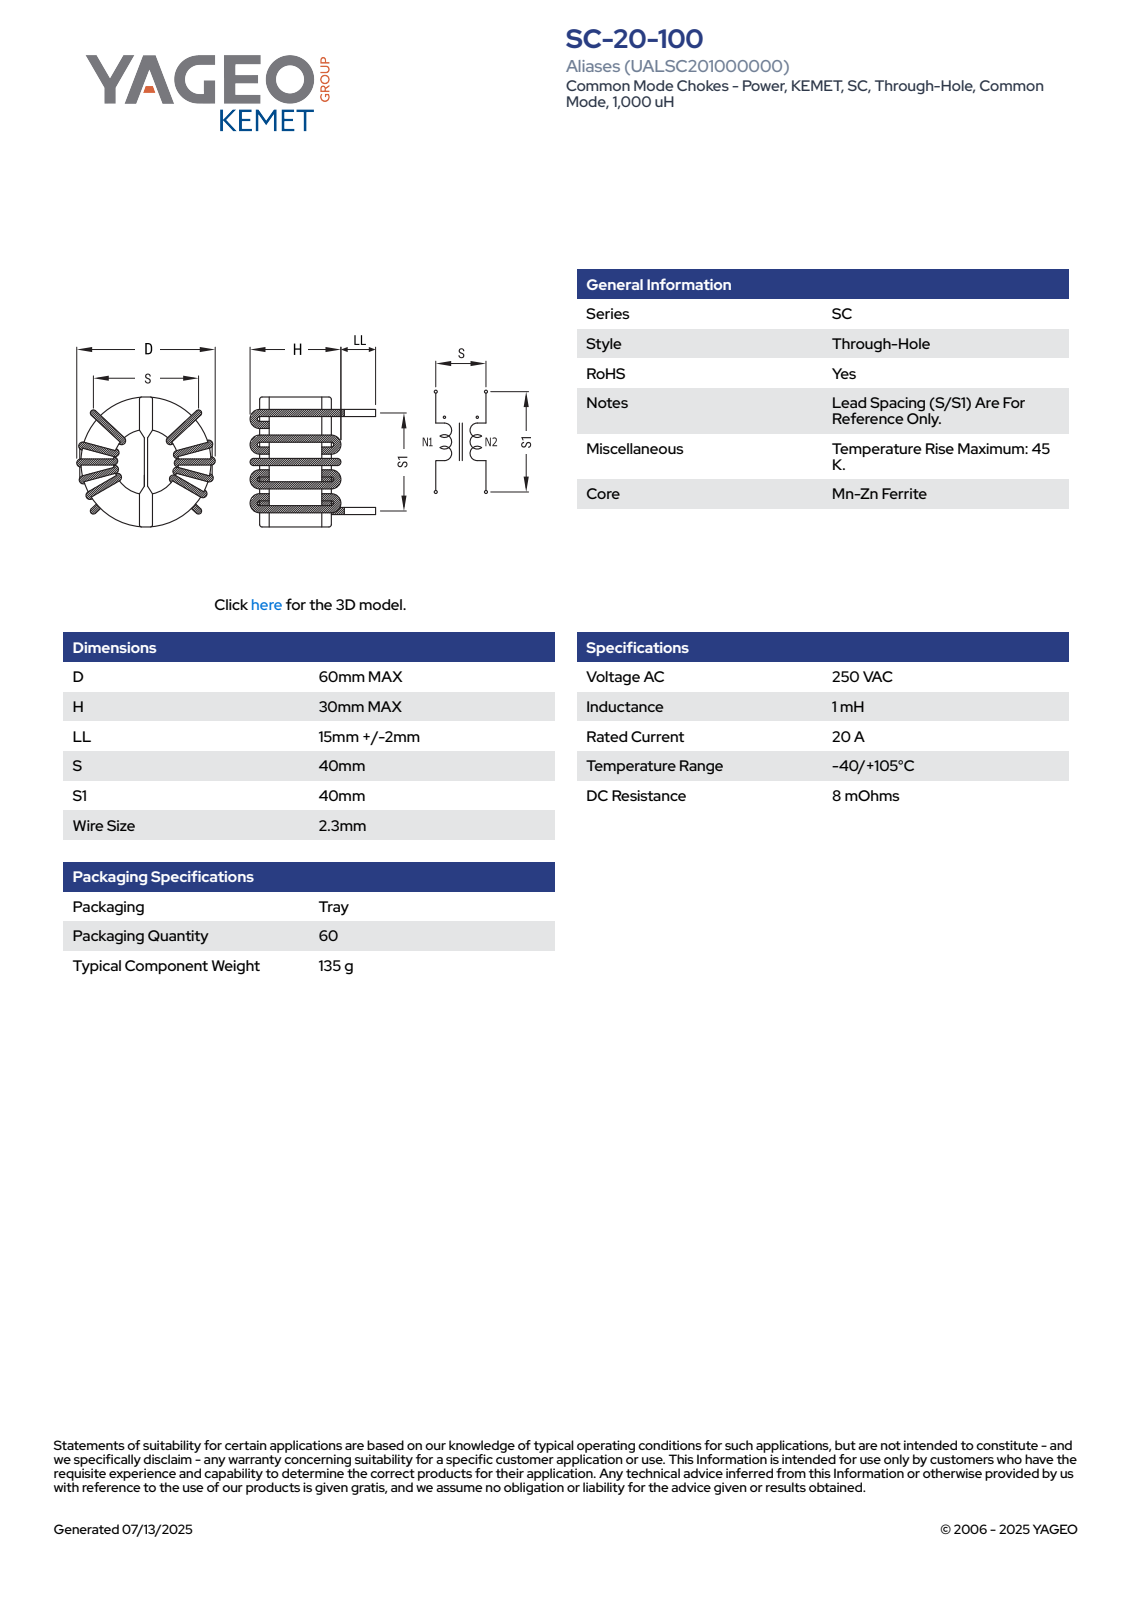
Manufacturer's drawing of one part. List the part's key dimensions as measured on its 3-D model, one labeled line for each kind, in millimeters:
Part name (STEP PRODUCT): SC-20-100
STEP written by: SolidWorks 2018 (AUTOMOTIVE_DESIGN)
Units: millimetres
Bodies: 1 solid, 348 faces (141 planar, 101 cylindrical, 106 other)
Overall size (bounding box): 60 × 59.74 × 45
Volume: 66 794 mm³ · Surface area: 16 217 mm²
Round holes (diameter × count): ⌀16.9 ×1
Round bosses / shafts (diameter × count): ⌀2.3 ×8, ⌀60 ×1
Partial cylindrical surfaces — rounded edges, fillets, slot ends (radius × count): R1.15 ×34, R1.5 ×2, R13.15 ×1, R13.75 ×1, R23.5 ×1, R23.7 ×1, R24.6 ×1
Main face-to-face distances: 26.3, 1.2, 2, 0.8, 3.2, 1.85, 28.15, 1.15, 2.05, 0.85
